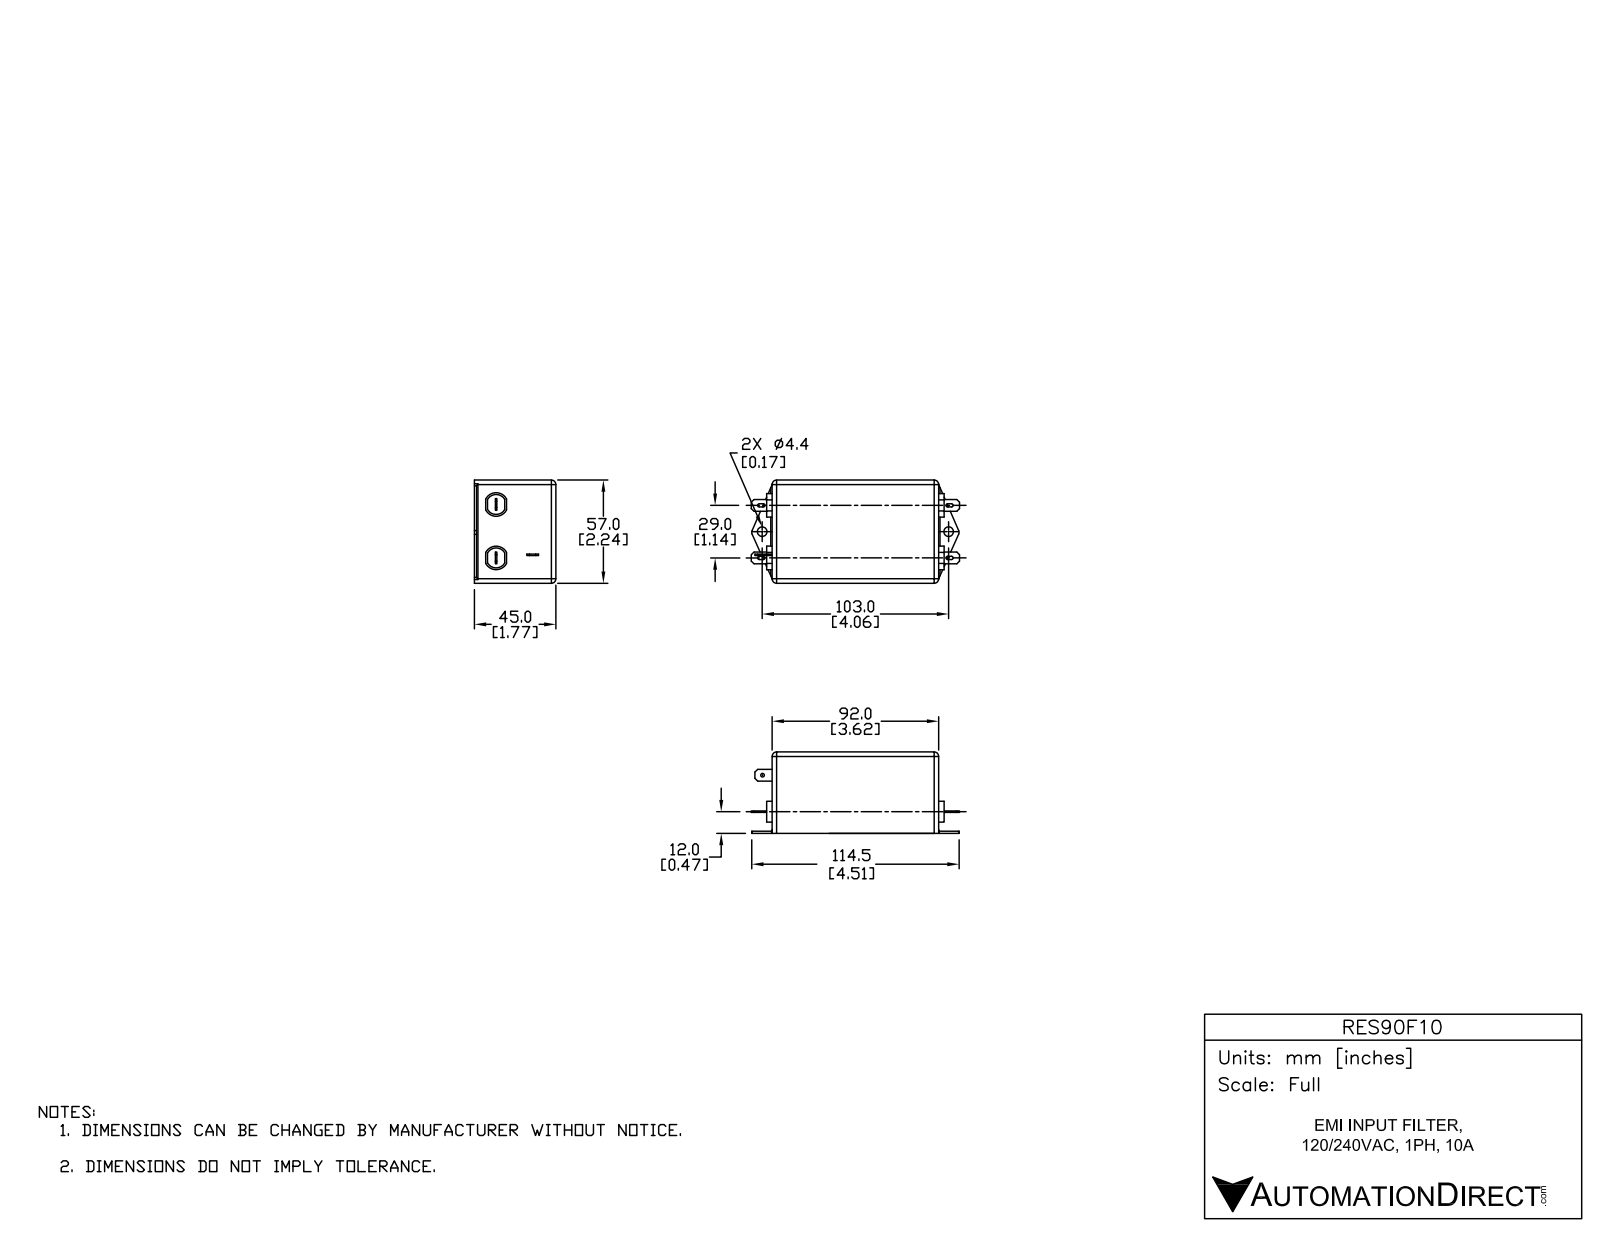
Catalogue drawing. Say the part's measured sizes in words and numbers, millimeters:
The part is named "RES90F10". Its 3-D file was written by "SolidWorks 2015 (AUTOMOTIVE_DESIGN)". It is 1 solid with 133 faces: 79 planar, 50 cylindrical and 4 other. Overall it measures 115 by 57 by 45 millimeters. Its volume is 237 234 cubic millimeters and its surface area 25 864 square millimeters. Round holes: 2 of diameter 5.3, 1 of diameter 2. Partial cylindrical surfaces (rounded edges, fillets, slot ends): 10 of radius 2.5, 8 of radius 0.88, 2 of radius 0.75, 2 of radius 5.5, 2 of radius 6.5. The main face-to-face distances are 45, 57, 92, 1.5, 1.2, 43.8, 93.5, 95, 0.8, 11.6. The hole center spacings are 103.
